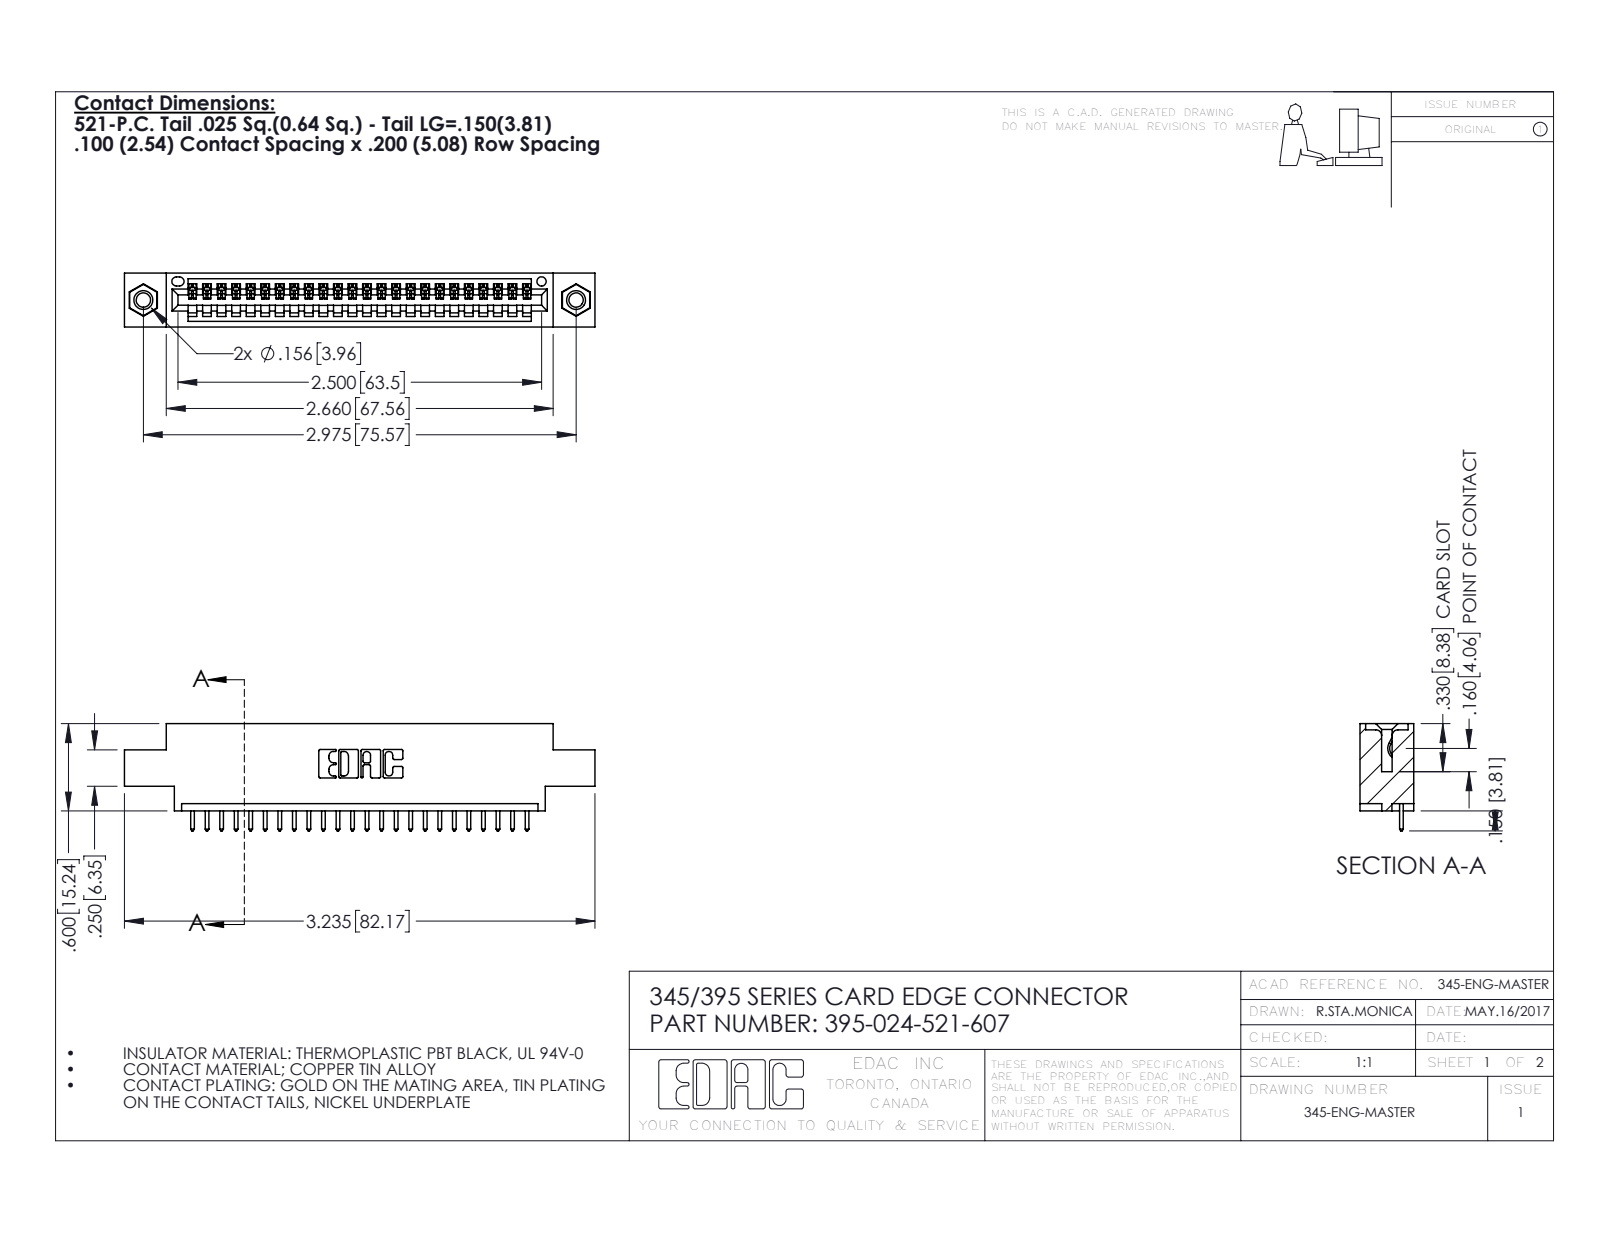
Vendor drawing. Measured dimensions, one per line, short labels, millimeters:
name: 345-250-001_345-250-005-103; 395-024-521-607; 345-292-001_345-293-121; 345 Part_0.170 Offset - 0.156 Dia-TI
written by: SolidWorks 2016 (CONFIG_CONTROL_DESIGN)
unit: mm
bodies: 27 solids, 1582 faces (1076 planar, 490 cylindrical, 16 other)
size: 82.2 × 18.7 × 9.4
volume: 7 460 mm³; area: 9 561 mm²
holes: 2× ⌀2.5, 2× ⌀3.2, 2× ⌀4, 1× ⌀1.6
bosses: 2× ⌀3.9
rounds: 48× R0.2, 48× R0.3, 22× R0.3, 6× R0.2, 6× R0.8, 3× R0.7, 2× R0.8, 2× R1
face distances: 1.8, 7.6, 9.4, 5.1, 2.5, 6.9, 0.6, 5.7, 4.4, 3.8
hole spacings: 6.9, 69.6, 75.6
